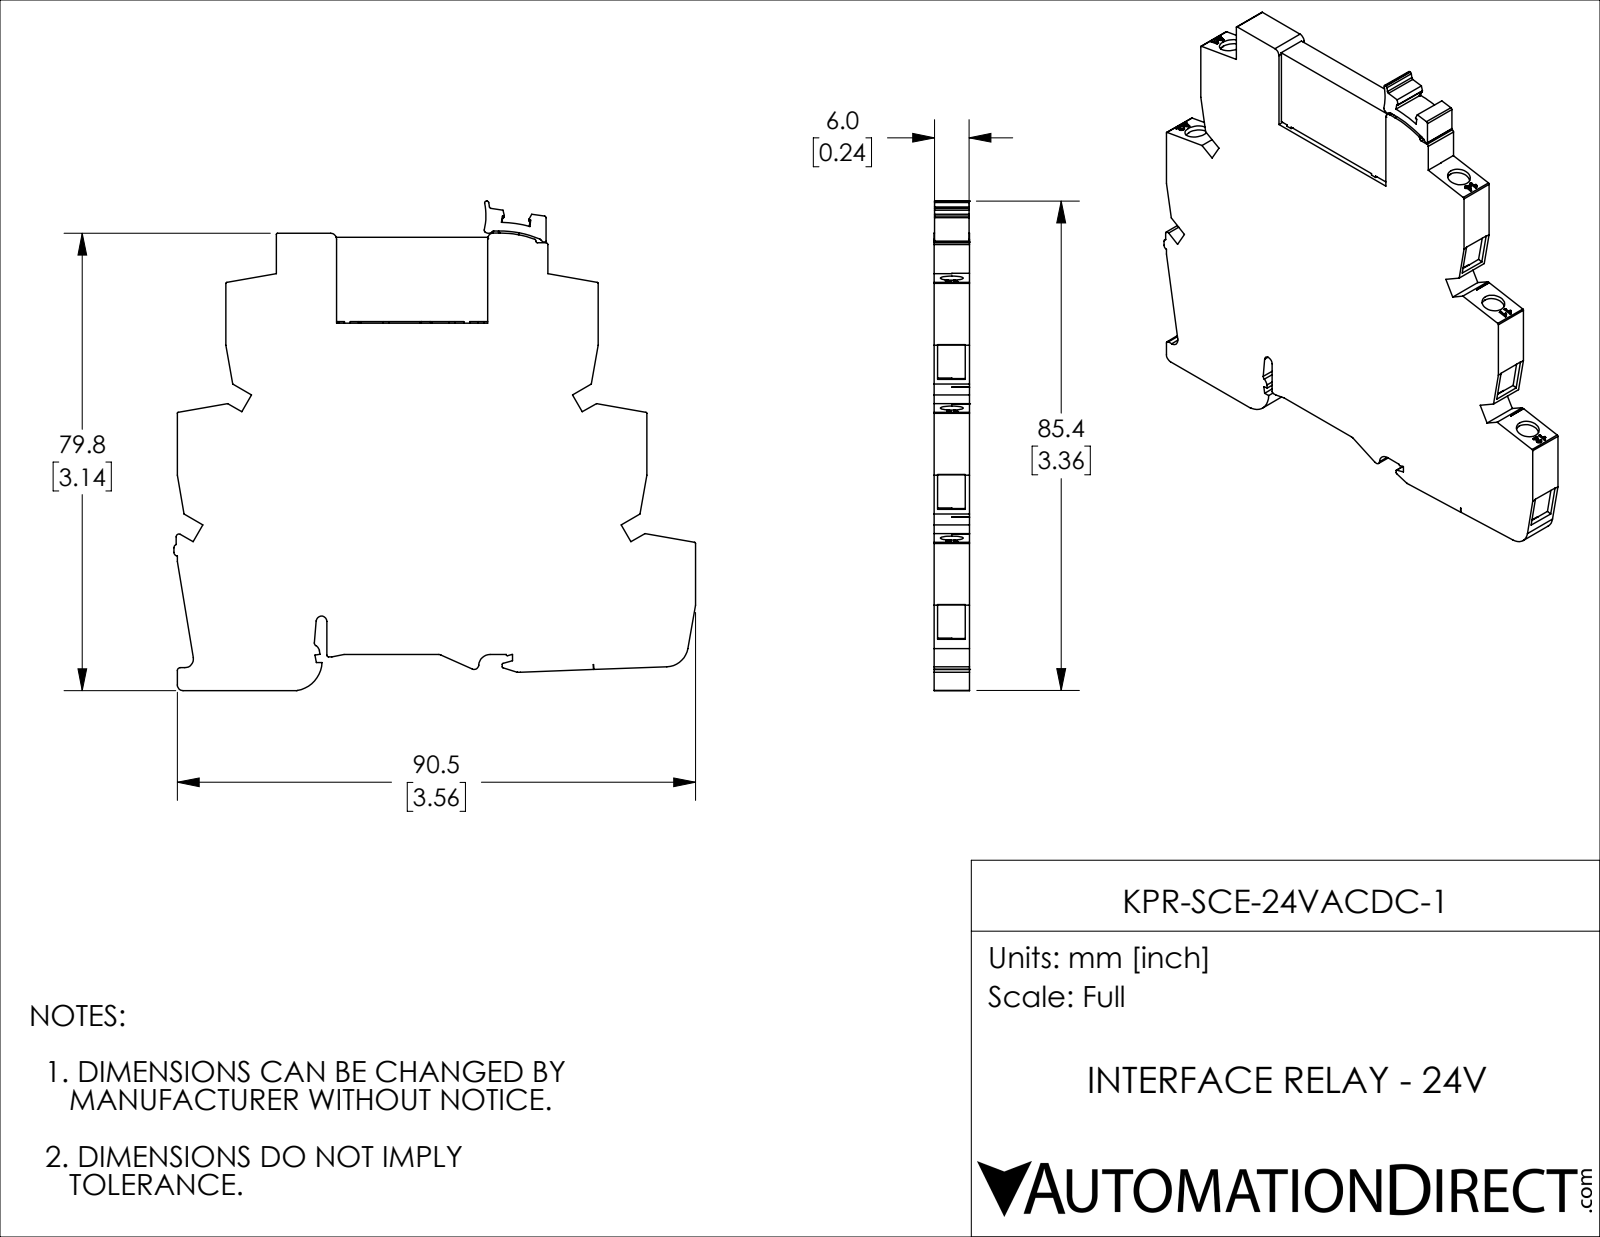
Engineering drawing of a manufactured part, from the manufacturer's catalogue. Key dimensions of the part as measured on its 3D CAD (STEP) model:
Part name (STEP PRODUCT): KPR-SCE-24VACDC-1
STEP written by: SolidWorks 2018 (AUTOMOTIVE_DESIGN)
Units: inches
Bodies: 1 solid, 422 faces (304 planar, 90 cylindrical, 28 other)
Overall size (bounding box): 3.586 × 3.364 × 0.244
Volume: 2.104 in³ · Surface area: 23.55 in²
Round holes (diameter × count): ⌀0.157 ×5
Round bosses / shafts (diameter × count): ⌀0.016 ×2
Partial cylindrical surfaces — rounded edges, fillets, slot ends (radius × count): R0.008 ×15, R0.012 ×10, R0.039 ×10, R0.02 ×5, R0.037 ×5, R0.079 ×3, R0.004 ×2, R0.024 ×2
Main face-to-face distances: 0.244, 0.024, 0.22, 0.033, 0.197, 0.335, 0.031, 0.821, 3.228, 2.894
Hole centre spacings: 0.485, 0.485, 0.969
